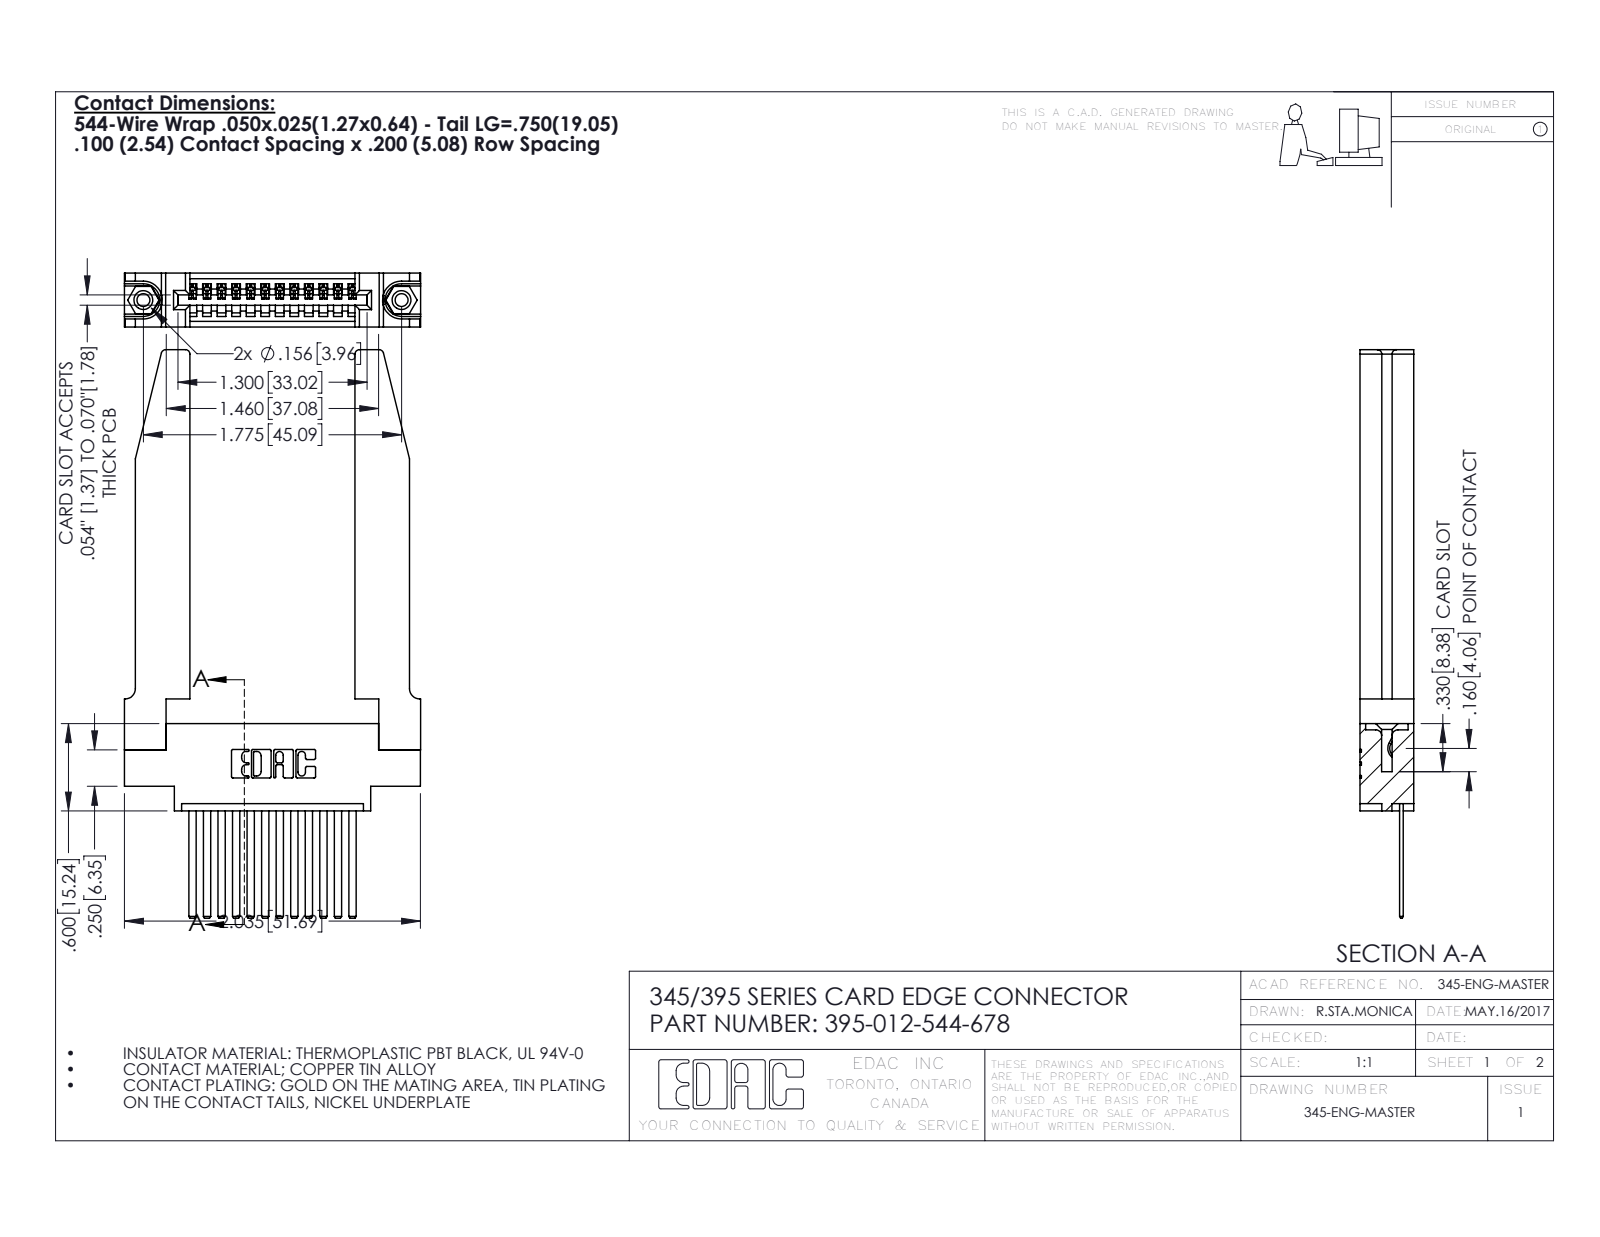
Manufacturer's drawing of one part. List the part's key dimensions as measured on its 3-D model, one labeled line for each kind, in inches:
Part name (STEP PRODUCT): 345-220-078_345-220-078; 345-250-001_345-250-001-102; 395-012-544-678; 345 Part_0.170 Offset - 0.156 Dia-TH (+1 more)
STEP written by: SolidWorks 2016 (CONFIG_CONTROL_DESIGN)
Units: inches
Bodies: 17 solids, 988 faces (658 planar, 278 cylindrical, 52 other)
Overall size (bounding box): 3.907 × 2.036 × 0.37
Volume: 0.76 in³ · Surface area: 20.49 in²
Round holes (diameter × count): ⌀0.089 ×2, ⌀0.125 ×2, ⌀0.156 ×2, ⌀0.064 ×1
Round bosses / shafts (diameter × count): ⌀0.155 ×2
Partial cylindrical surfaces — rounded edges, fillets, slot ends (radius × count): R0.006 ×24, R0.01 ×22, R0.03 ×8, R0.007 ×6, R0.031 ×6, R0.026 ×3, R0.031 ×2, R0.04 ×2
Main face-to-face distances: 0.37, 0.072, 0.298, 0.098, 0.272, 0.025, 0.15, 0.148, 0.22, 0.077
Hole centre spacings: 0.27, 1.543, 1.775
